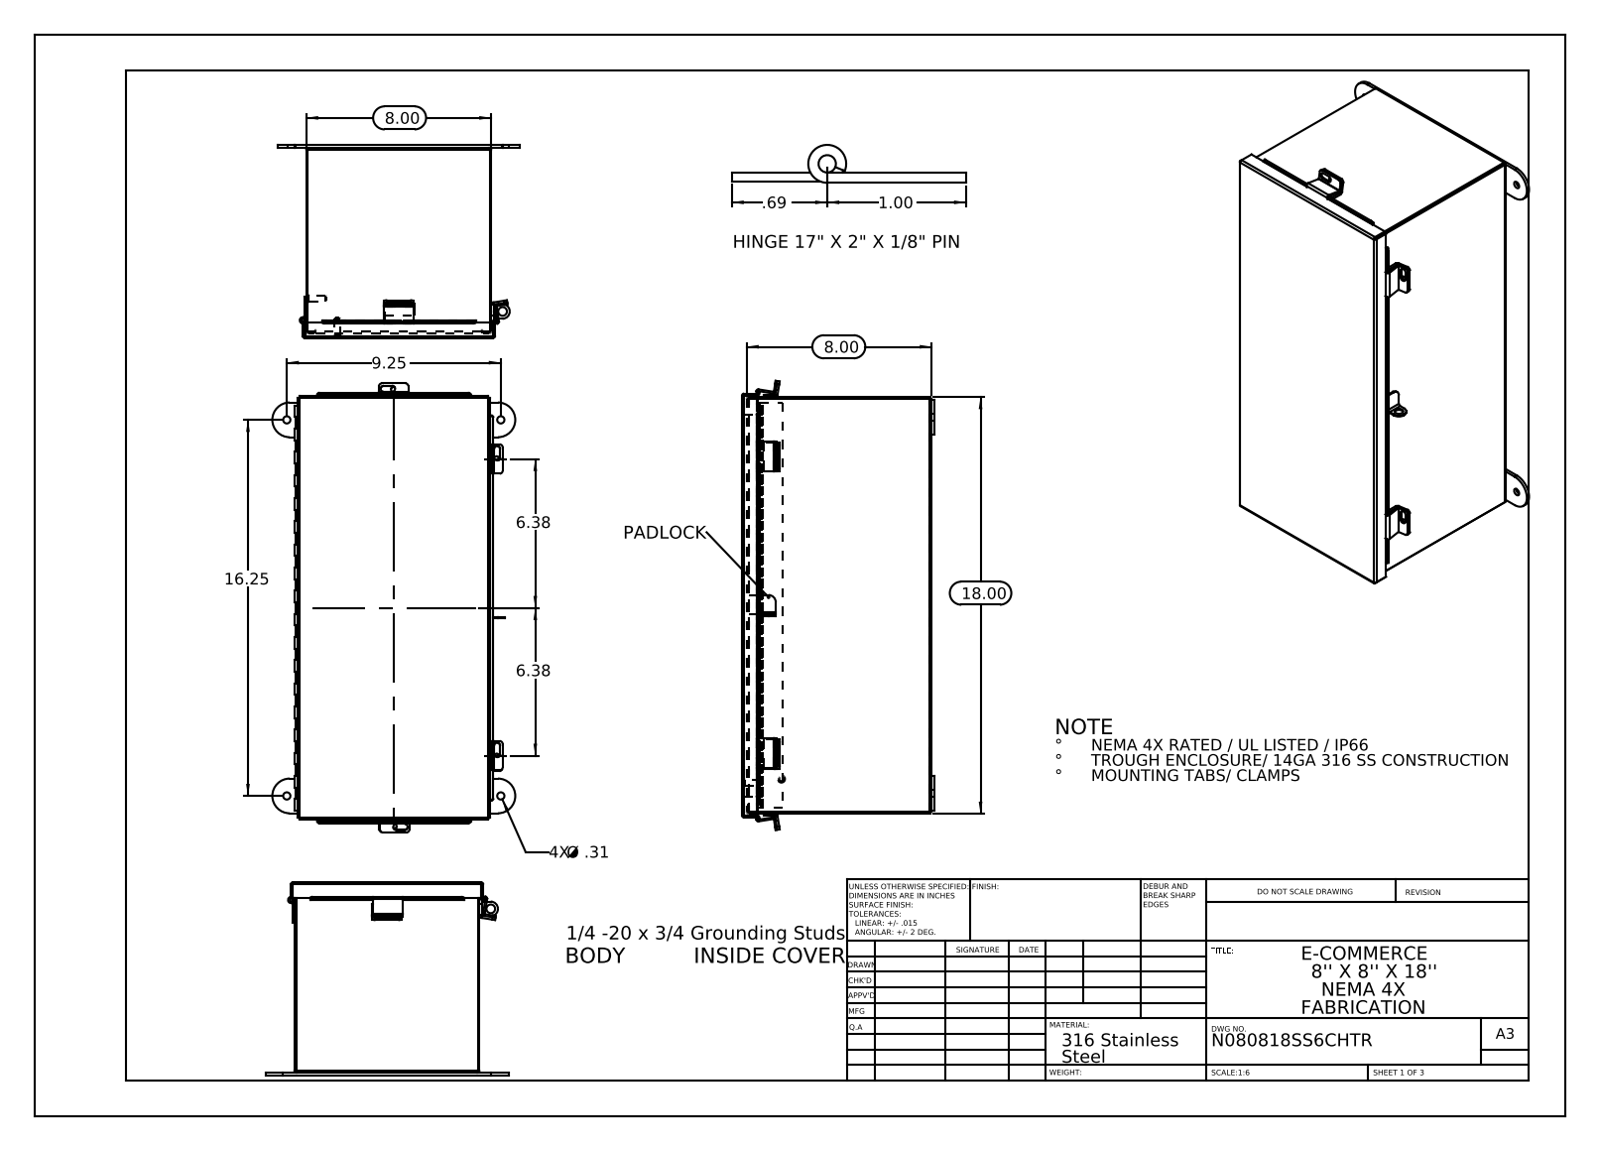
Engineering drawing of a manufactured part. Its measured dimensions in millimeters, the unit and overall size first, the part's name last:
Units: millimetres
Overall size (bounding box): 492.9 × 266.7 × 211.8
Round holes (diameter × count): ⌀6.4 ×4, ⌀8 ×4, ⌀3.2 ×1, ⌀3.2 ×1, ⌀9.5 ×1
Round bosses / shafts (diameter × count): ⌀8 ×2, ⌀6 ×2, ⌀6.9 ×1, ⌀6.4 ×1
Partial cylindrical surfaces — rounded edges, fillets, slot ends (radius × count): R3.2 ×15, R0.2 ×12, R0.3 ×10, R2.2 ×10, R3.4 ×8, R2.1 ×6, R2.5 ×6, R19.1 ×4
Main face-to-face distances: 1.9, 201.3, 206.5, 199.4, 203.2, 208.4, 204.5, 455.3, 453.4, 457.2
Hole centre spacings: 235, 412.8, 474.9, 219.3, 326.4
Volume: 1 046 000 mm³ · Surface area: 1 094 000 mm²
Bodies: 19 solids, 744 faces (461 planar, 263 cylindrical, 20 other)
Part name (STEP PRODUCT): N080818SSCHTR Hinge Body Side; N080818SSCHTR _JIC Hinge; N080818SSCHTR JIC Top; N080818SSCHTR JIC Bottom (+8 more)
STEP written by: SolidWorks 2013 (CONFIG_CONTROL_DESIGN)
